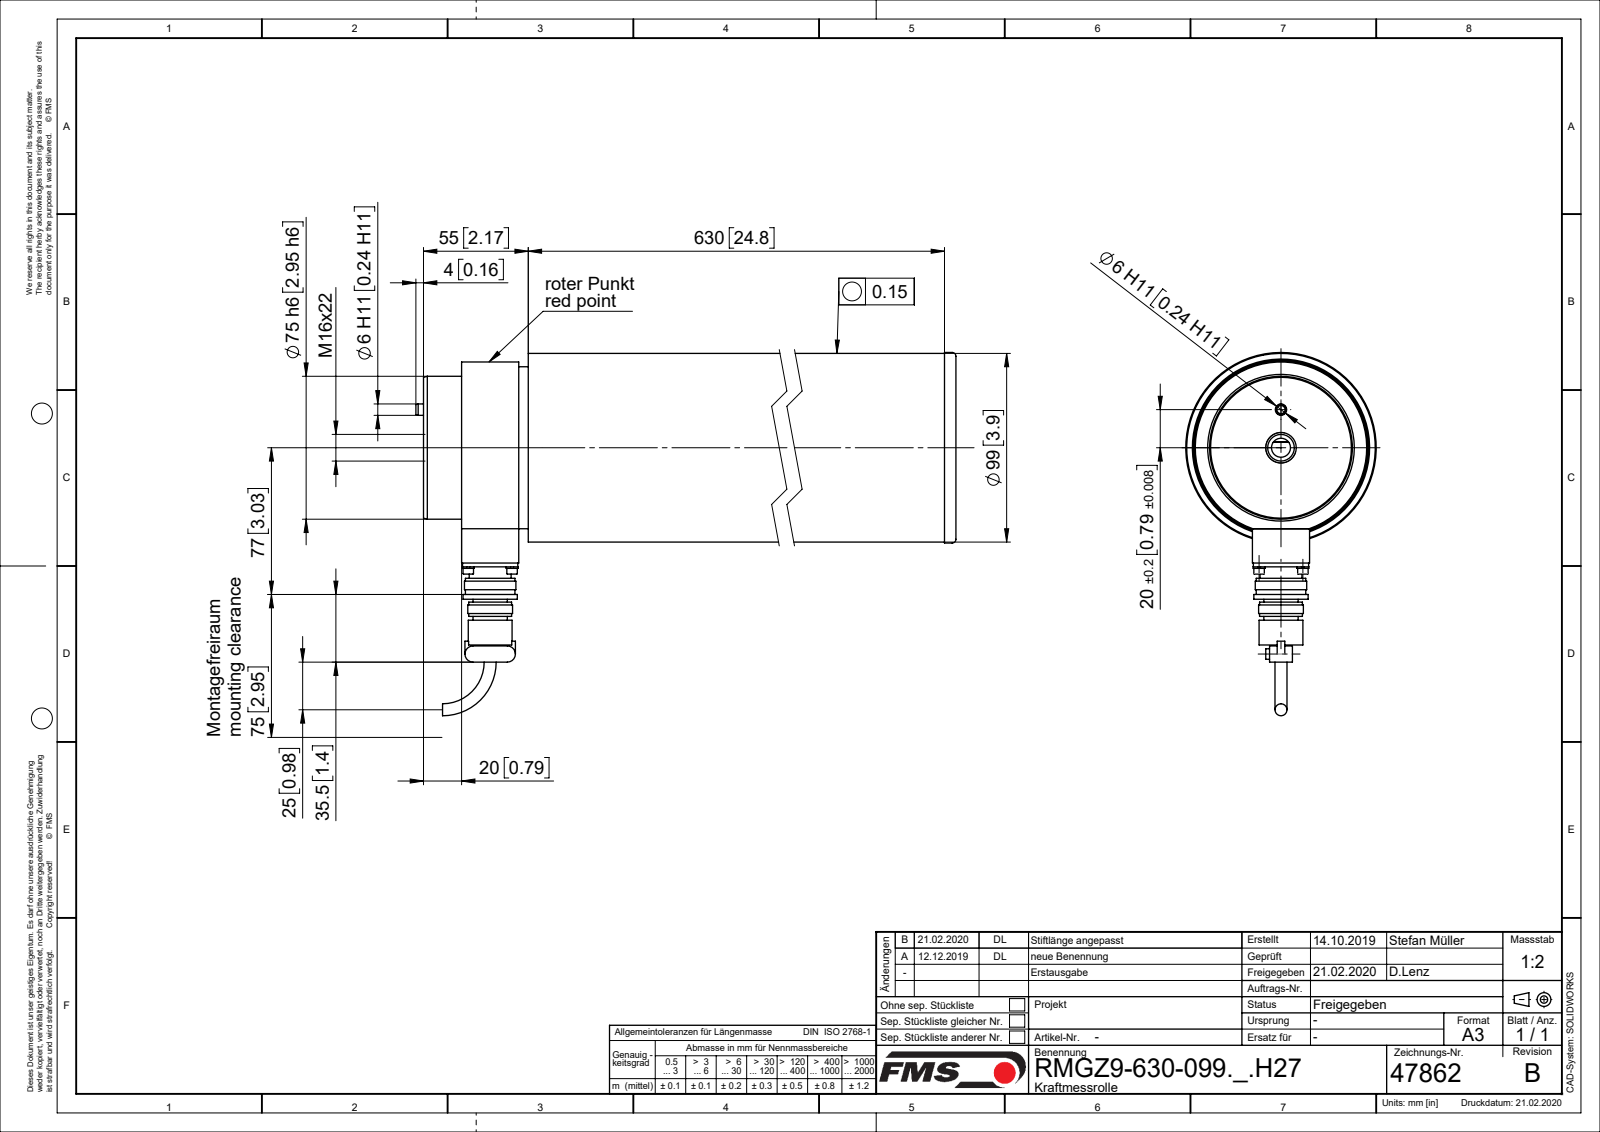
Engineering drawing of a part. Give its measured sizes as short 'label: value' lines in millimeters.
name: 130507.5_01; FLANSCHDOSE_14S-2P_4-POLIG; Zyl-Schr DIN912_M3x25; Spannstift_ISO13337_D06x12 (+8 more)
written by: SolidWorks 2018 (CONFIG_CONTROL_DESIGN)
unit: mm
bodies: 31 solids, 570 faces (162 planar, 234 cylindrical, 174 other)
size: 695 × 190.65 × 100
volume: 2 236 000 mm³; area: 630 378 mm²
holes: 4× ⌀2.5, 4× ⌀3.1, 4× ⌀3.4, 1× ⌀3.3, 1× ⌀5, 1× ⌀6, 1× ⌀10, 1× ⌀12, 1× ⌀14, 1× ⌀22, 1× ⌀23, 1× ⌀26
bosses: 6× ⌀5.5, 4× ⌀6.2, 4× ⌀3, 4× ⌀2.5, 1× ⌀100, 1× ⌀99, 1× ⌀91, 1× ⌀90
rounds: 4× R11, 2× R4.25, 1× R17.5
face distances: 50, 32, 156, 10, 225, 2, 35, 381, 414, 524
hole spacings: 16.26, 23, 32.53, 20
